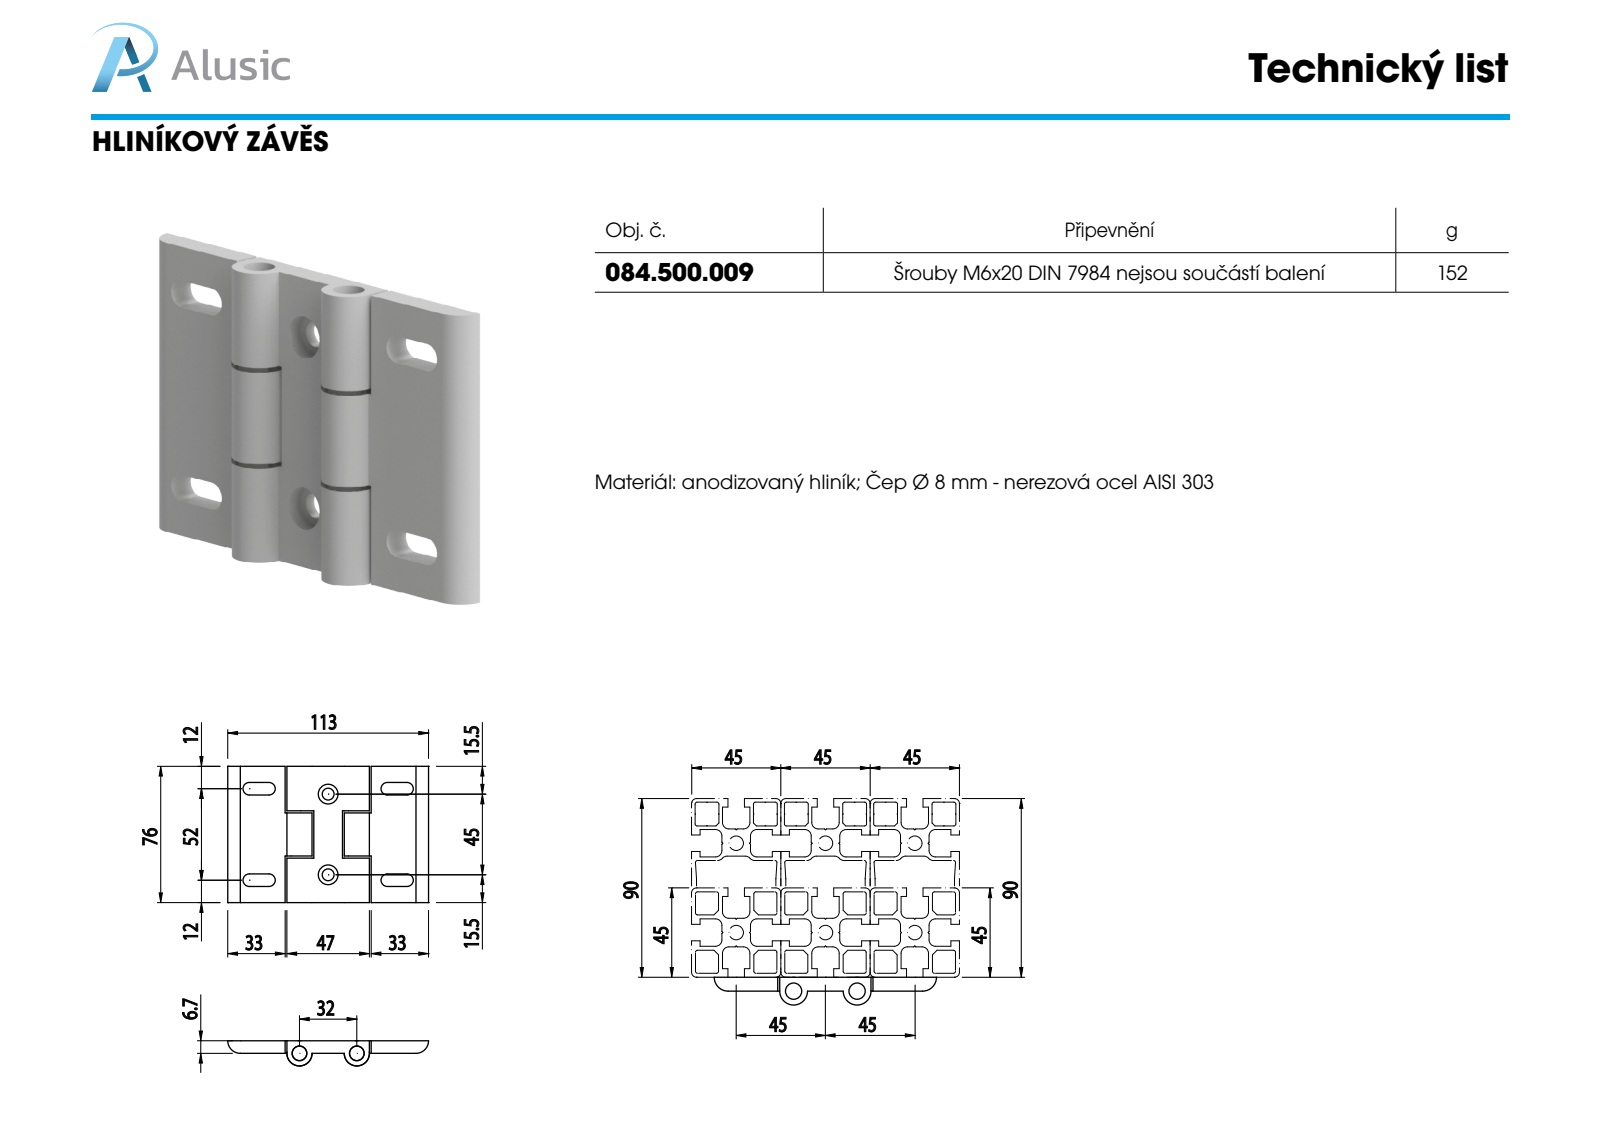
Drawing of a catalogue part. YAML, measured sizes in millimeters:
part_name: "084.500.009; 084.500.001.C; 084.500.008b_084.500.002.A; PRT68-2^PRT68"
step_written_by: "SolidWorks 2011 (CONFIG_CONTROL_DESIGN)"
units: millimeters
bodies: {solids: 7, faces: 106, planar: 48, cylindrical: 58, other: 0}
overall_size: [113, 76, 14.1]
volume: 54966
surface_area: 28541
round_holes:
  - {diameter: 6.6, count: 2}
  - {diameter: 8.1, count: 2}
  - {diameter: 8.2, count: 2}
  - {diameter: 11, count: 2}
round_bosses_or_shafts:
  - {diameter: 14.1, count: 2}
partial_cylinders:
  - {radius: 3.5, count: 8}
  - {radius: 6.7, count: 2}
  - {radius: 7, count: 2}
face_to_face_distances: [6.7, 7, 25.2, 76, 24.8, 51.2, 15.5, 26, 50, 0.51]
hole_center_spacings: [32, 45]
